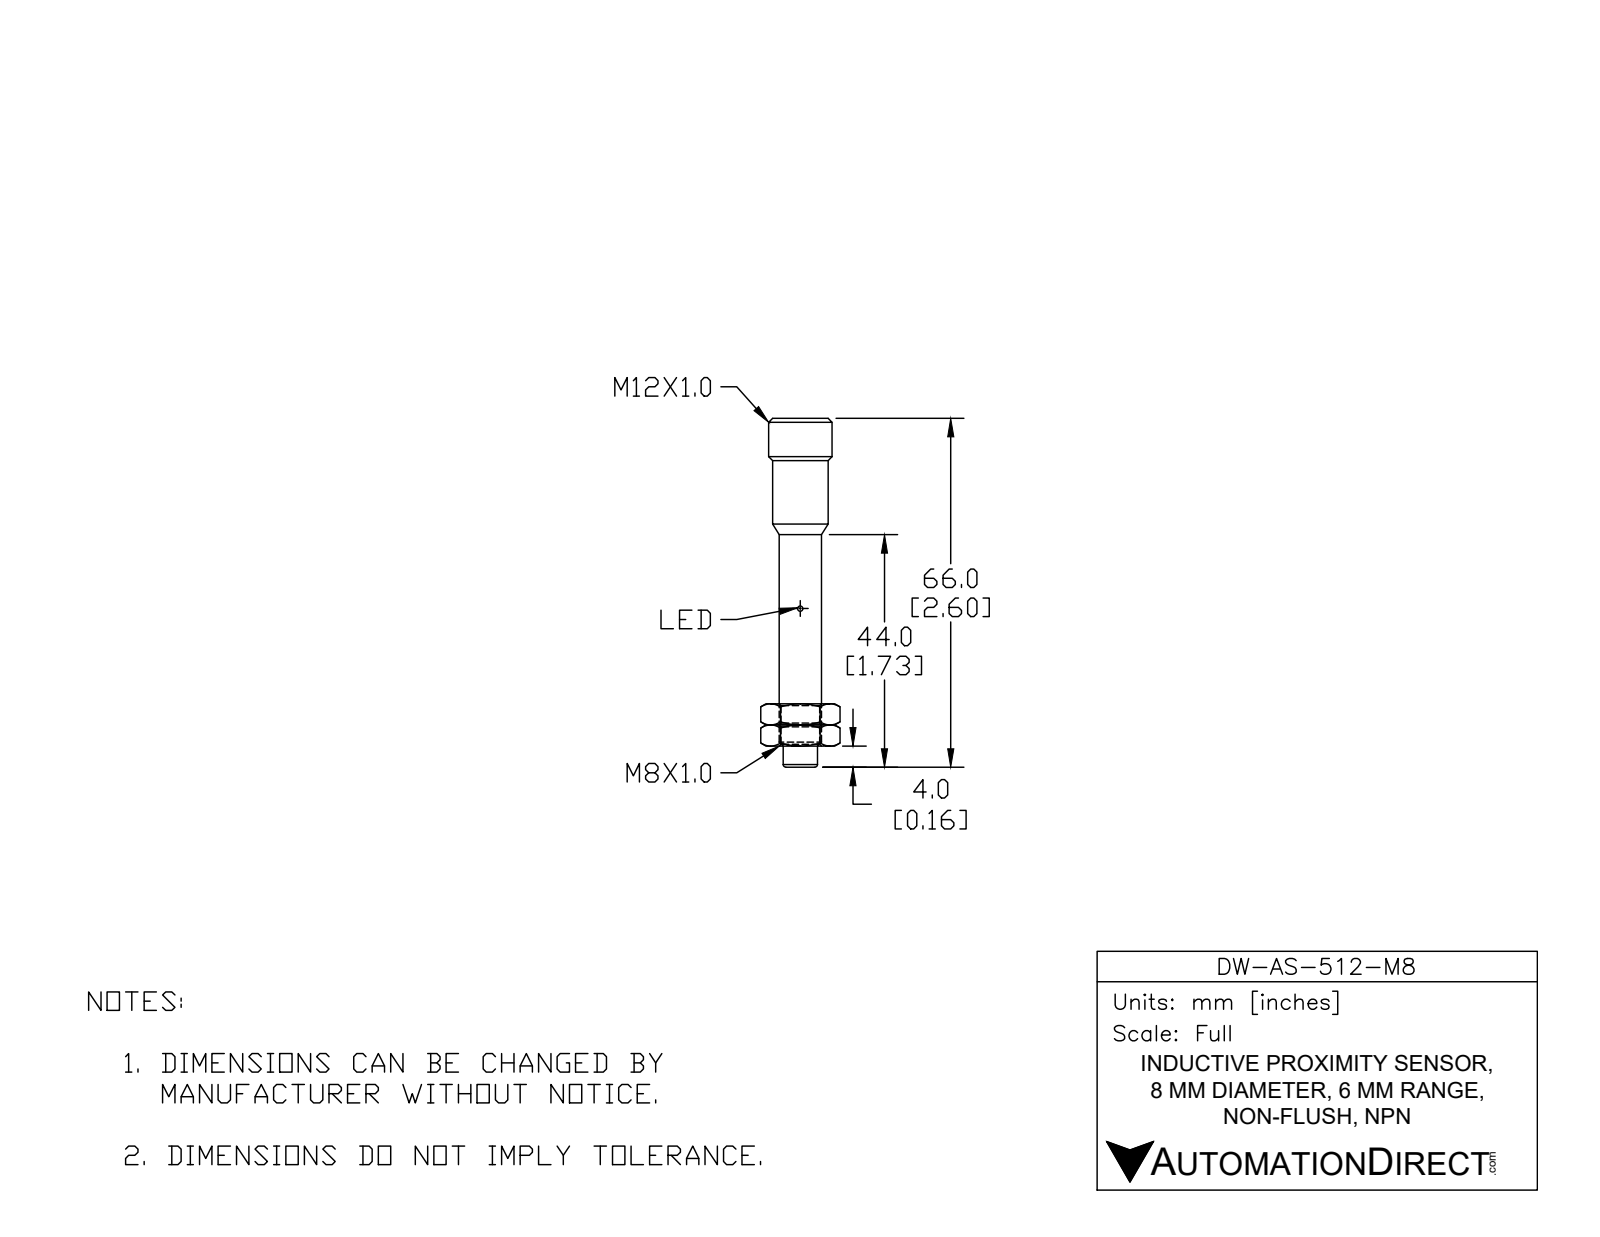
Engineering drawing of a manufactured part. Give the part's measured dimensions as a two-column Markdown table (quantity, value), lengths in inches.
| quantity | value |
| --- | --- |
| part name | DW-AS-512-M8 |
| STEP written by | SolidWorks 2017 (AUTOMOTIVE_DESIGN) |
| units | inches |
| bodies | 1 solid, 35 faces (10 planar, 17 cylindrical, 8 other) |
| overall size | 2.599 × 0.472 × 0.472 |
| volume | 0.225 in³ |
| surface area | 3.685 in² |
| round holes (diameter × count) | 0.12 × 2 |
| round bosses / shafts (diameter × count) | 0.039 × 4, 0.472 × 1, 0.415 × 1, 0.335 × 1, 0.315 × 1, 0.272 × 1 |
| main face-to-face distances | 0.343, 2.256, 2.598, 1.811, 0.445, 0.787, 0.165, 1.646, 2.091, 2.433 |
